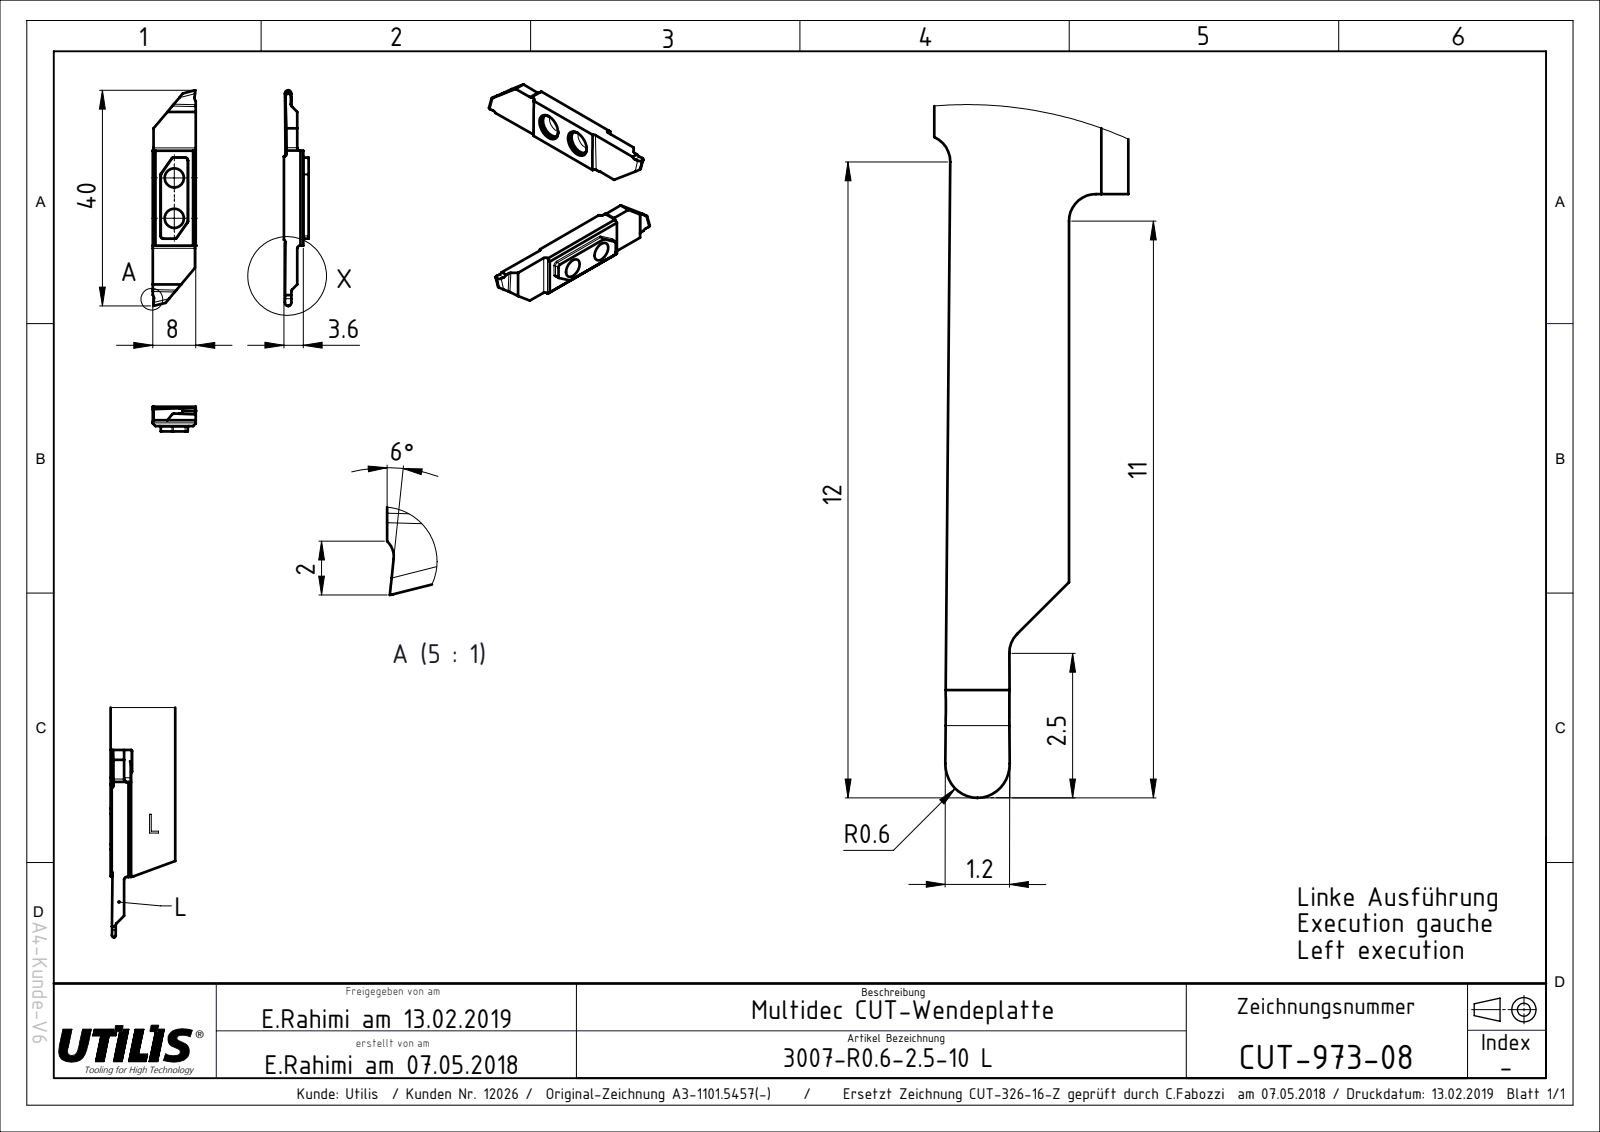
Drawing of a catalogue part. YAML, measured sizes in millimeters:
part_name: "CUT-973; ASME Y14.5"
step_written_by: "FormatWorks Professional (AP242_MANAGED_MODEL_BASED_3D_ENGINEERING_MIM_LF)"
units: millimeters
bodies: {solids: 1, faces: 40, planar: 22, cylindrical: 18, other: 0}
overall_size: [40, 8, 3.6]
volume: 702
surface_area: 820
round_holes:
  - {diameter: 3.55, count: 2}
partial_cylinders:
  - {radius: 0.5, count: 6}
  - {radius: 0.6, count: 2}
  - {radius: 0.8, count: 2}
  - {radius: 1, count: 2}
face_to_face_distances: [3.6, 2.5, 1.1, 8, 7.85, 22.54, 0.86, 7.7, 17.6, 7.58]
hole_center_spacings: [7.5]
